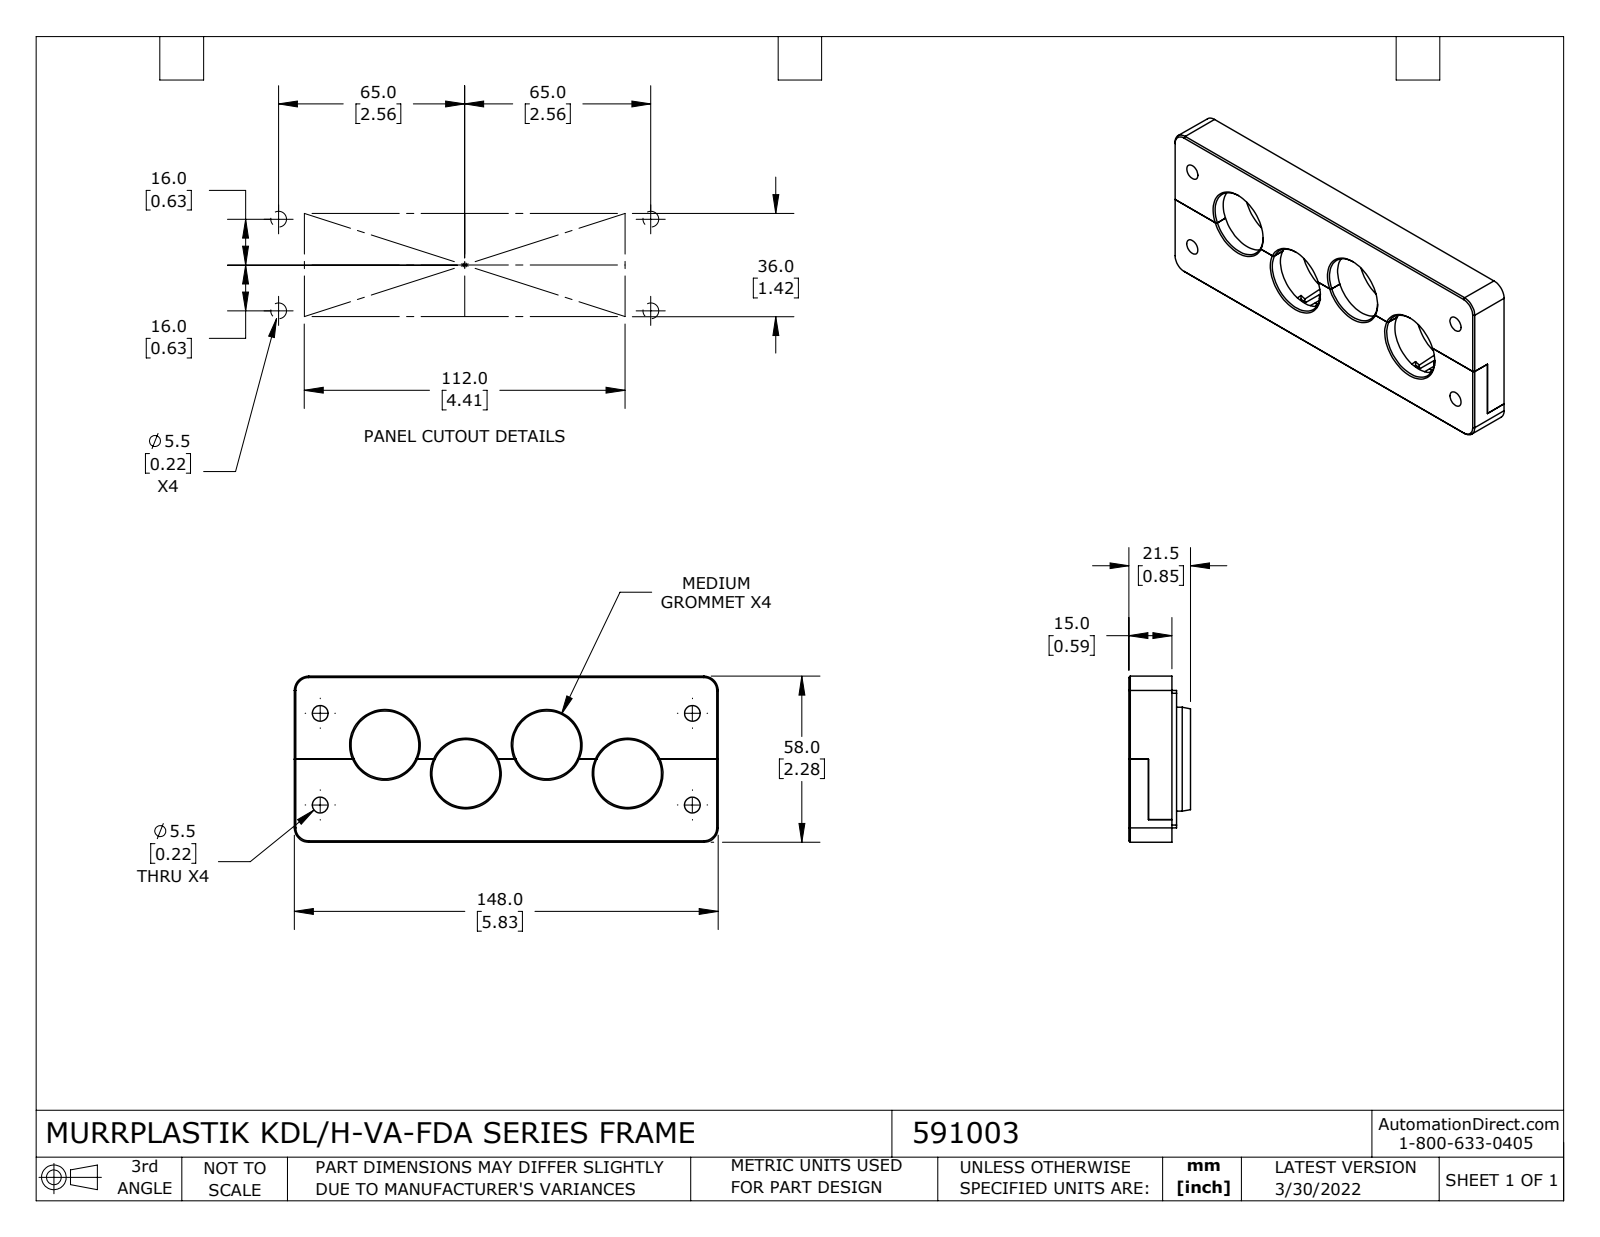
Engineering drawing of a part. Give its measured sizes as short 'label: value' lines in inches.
name: 591003
written by: SolidWorks 2021 (CONFIG_CONTROL_DESIGN)
unit: in
bodies: 3 solids, 514 faces (255 planar, 145 cylindrical, 114 other)
size: 5.827 × 2.283 × 0.846
volume: 6.314 in³; area: 76.69 in²
holes: 4× ⌀0.217, 4× ⌀0.933, 4× ⌀0.982, 2× ⌀0.236, 2× ⌀0.335
bosses: 2× ⌀0.291
rounds: 20× R0.039, 8× R0.098, 6× R0.02, 4× R0.004, 4× R0.006, 4× R0.012, 4× R0.016, 4× R0.197
face distances: 0.177, 0.197, 0.02, 2.087, 2.106, 1.909, 0.157, 0.413, 0.65, 0.472
hole spacings: 1.18, 0.394, 0.866, 0.991, 1.215, 1.248, 1.26, 2.05
